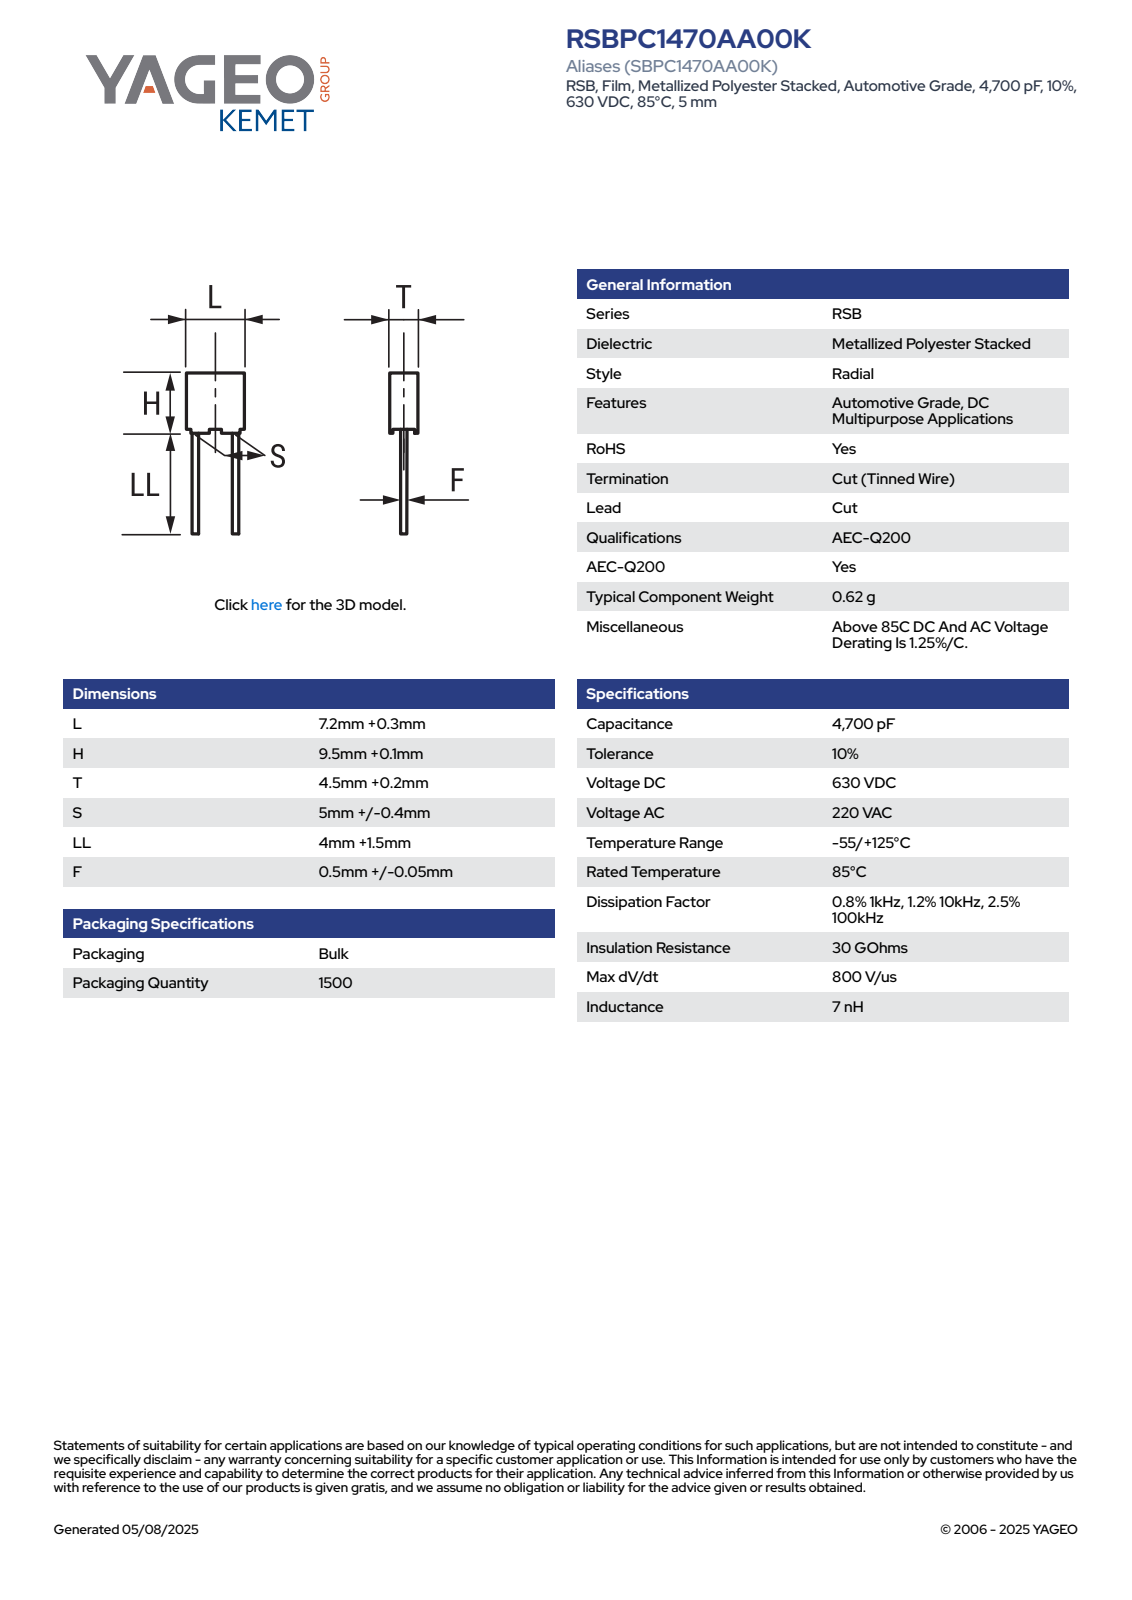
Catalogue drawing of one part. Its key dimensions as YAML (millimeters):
part_name: "CFR_RB3_7.2X9.5X4.5_L7.5H9.6T4.7S5LL5.5F0.65"
step_written_by: "SolidWorks 2014 (AUTOMOTIVE_DESIGN)"
units: millimeters
bodies: {solids: 4, faces: 85, planar: 77, cylindrical: 8, other: 0}
overall_size: [15.1, 7.5, 4.71]
volume: 319
surface_area: 344
round_bosses_or_shafts:
  - {diameter: 0.65, count: 2}
partial_cylinders:
  - {radius: 0.5, count: 4}
face_to_face_distances: [4.7, 7.5, 8.85, 4.45, 7.25, 0.75, 9.6, 4.2, 7, 4.71]
